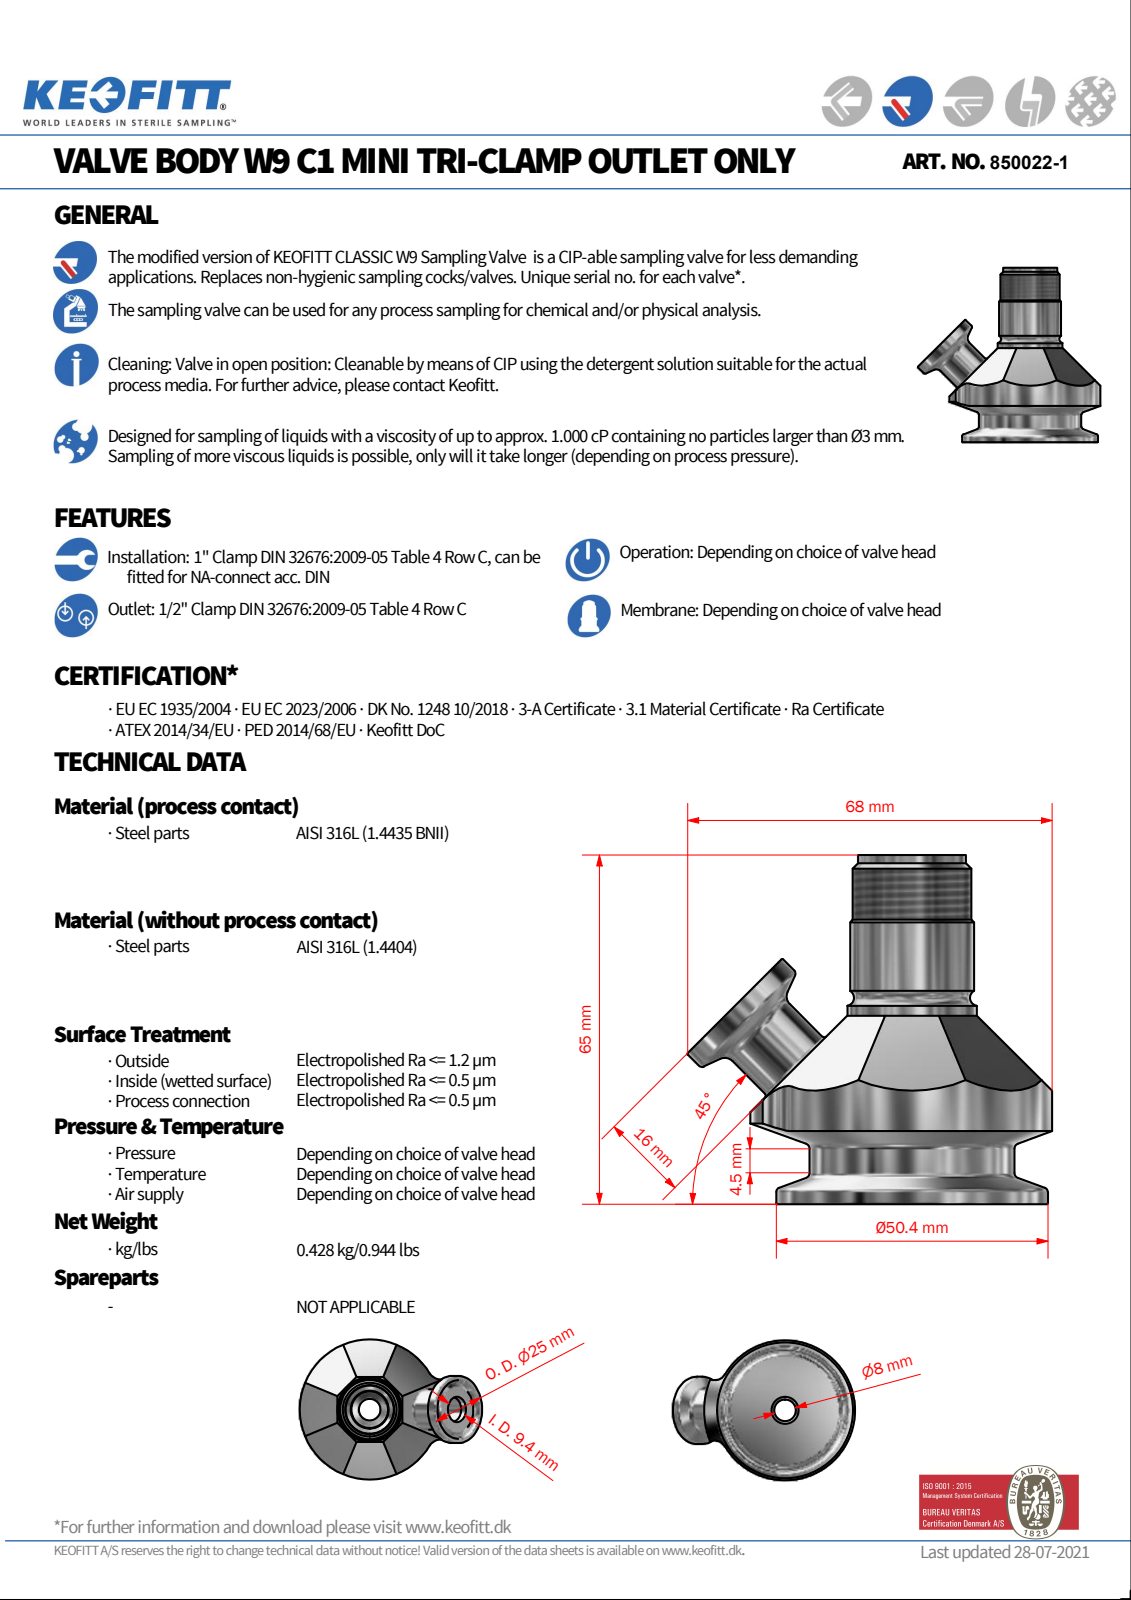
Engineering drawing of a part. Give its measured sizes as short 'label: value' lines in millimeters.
name: 850022-1
written by: Autodesk Inventor 2022 (AUTOMOTIVE_DESIGN)
unit: mm
bodies: 2 solids, 71 faces (21 planar, 22 cylindrical, 28 other)
size: 67.67 × 64.8 × 52
volume: 67 053 mm³; area: 19 263 mm²
holes: 1× ⌀9, 1× ⌀18.1, 1× ⌀21, 1× ⌀21.8
bosses: 1× ⌀52, 1× ⌀50.4, 1× ⌀38, 1× ⌀25, 1× ⌀24, 1× ⌀23, 1× ⌀22, 1× ⌀20.5
rounds: 2× R4.5, 1× R30
face distances: 59.3, 15.2, 34.8, 24.5, 29, 5.8, 30.3, 35, 6, 24.3
